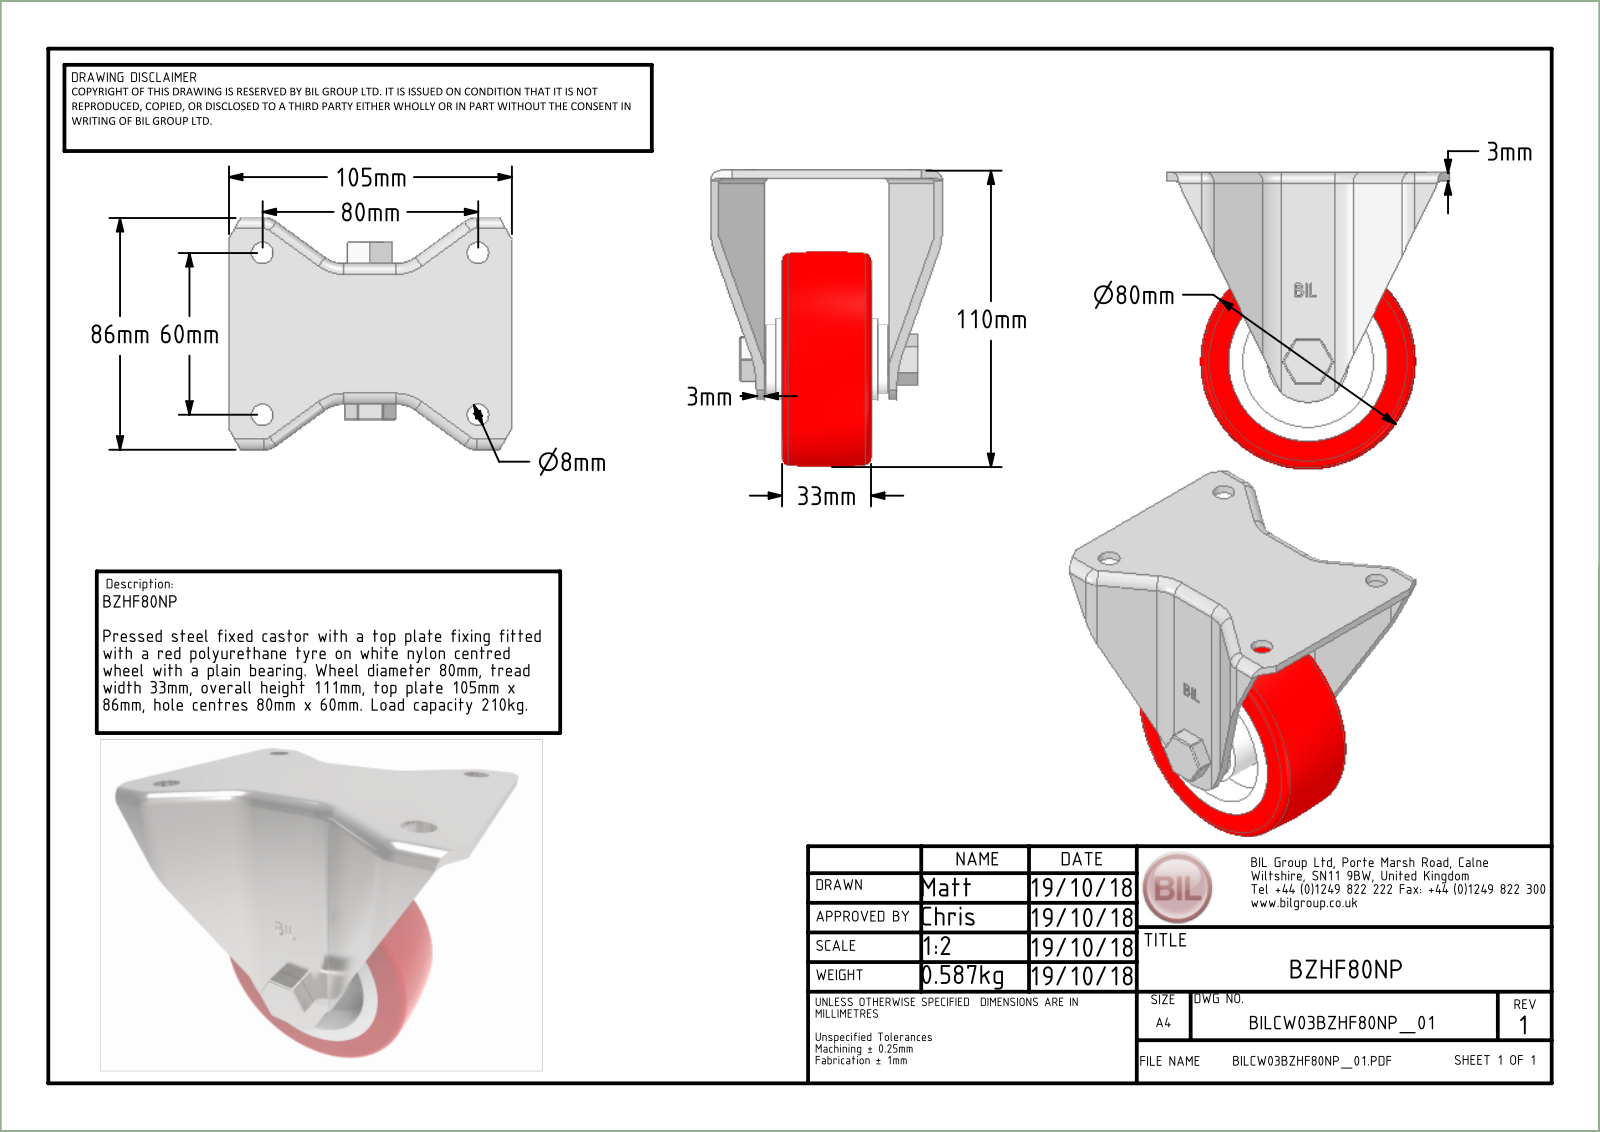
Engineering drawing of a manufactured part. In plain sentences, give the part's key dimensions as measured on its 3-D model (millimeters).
The part is named "BZHF80NP v3; BZHF80AS v1; BZHF80AS; ZINC PLATED, PRESSED STEEL BRACKET (+8 more)". Its 3-D file was written by "Autodesk Translation Framework v14.10.0.0 (AUTOMOTIVE_DESIGN)". It is 7 solids with 405 faces: 150 planar, 141 cylindrical and 114 other. Overall it measures 110 by 105 by 86 millimeters. Its volume is 198 403 cubic millimeters and its surface area 81 067 square millimeters. Round holes: 1 of diameter 10, 1 of diameter 10.2, 1 of diameter 12, 1 of diameter 12.5, 1 of diameter 58. Round bosses or shafts: 1 of diameter 26, 1 of diameter 16, 1 of diameter 15.5, 1 of diameter 11.95, 1 of diameter 9.85, 1 of diameter 8.14. Partial cylindrical surfaces (rounded edges, fillets, slot ends): 18 of radius 0.5, 12 of radius 0.75, 12 of radius 3, 10 of radius 1.5, 9 of radius 10, 8 of radius 4.5, 4 of radius 7, 4 of radius 13. The main face-to-face distances are 3, 2, 44.5, 41.5, 51, 11.5, 53, 8.5, 33, 19.5.
